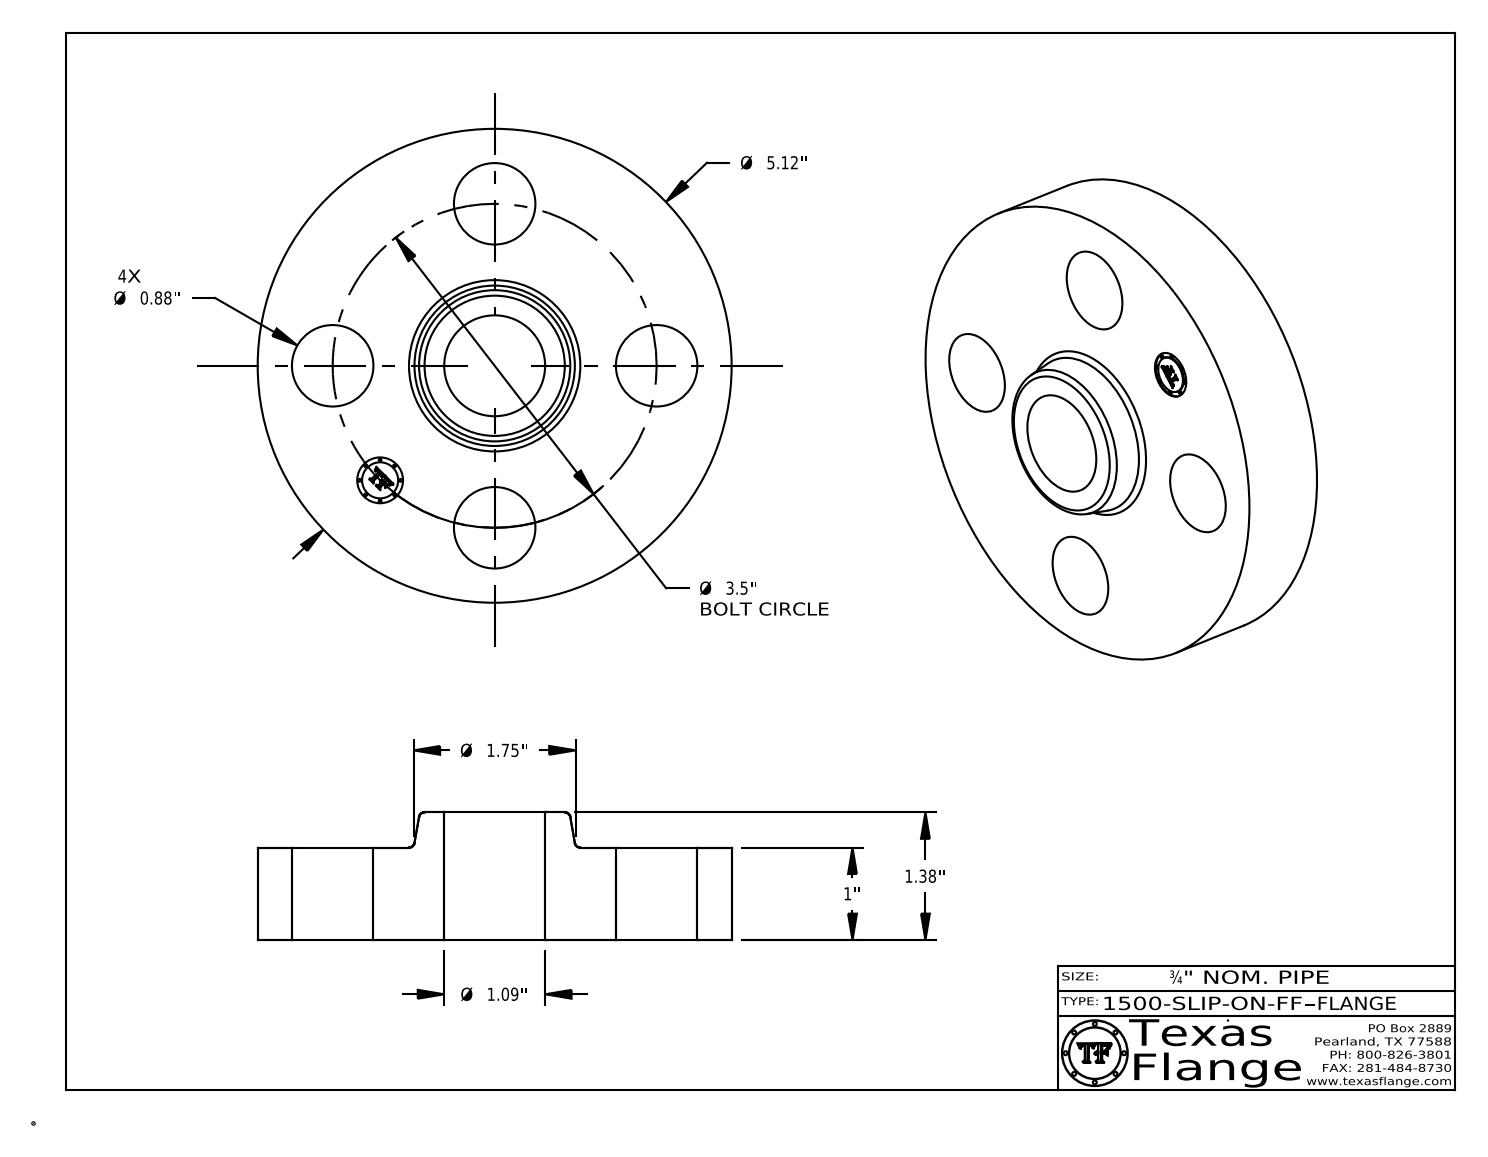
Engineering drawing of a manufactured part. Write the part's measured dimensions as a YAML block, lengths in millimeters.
part_name: "1500-SLIP-ON-FF"
step_written_by: "CATIA V5 STEP AP214 (AUTOMOTIVE_DESIGN)"
units: millimeters
bodies: {solids: 1, faces: 406, planar: 368, cylindrical: 32, other: 6}
overall_size: [130, 130, 35.1]
volume: 290200
surface_area: 43810
round_holes:
  - {diameter: 22.4, count: 4}
  - {diameter: 12.6, count: 1}
  - {diameter: 27.7, count: 1}
round_bosses_or_shafts:
  - {diameter: 0.8, count: 8}
  - {diameter: 130, count: 1}
  - {diameter: 9.9, count: 1}
face_to_face_distances: [25.4, 35.1, 9.7, 0.4, 25, 10, 3.8, 3.7, 0.7, 2.4]
hole_center_spacings: [44.5, 62.9, 34, 82.1, 88.9]
